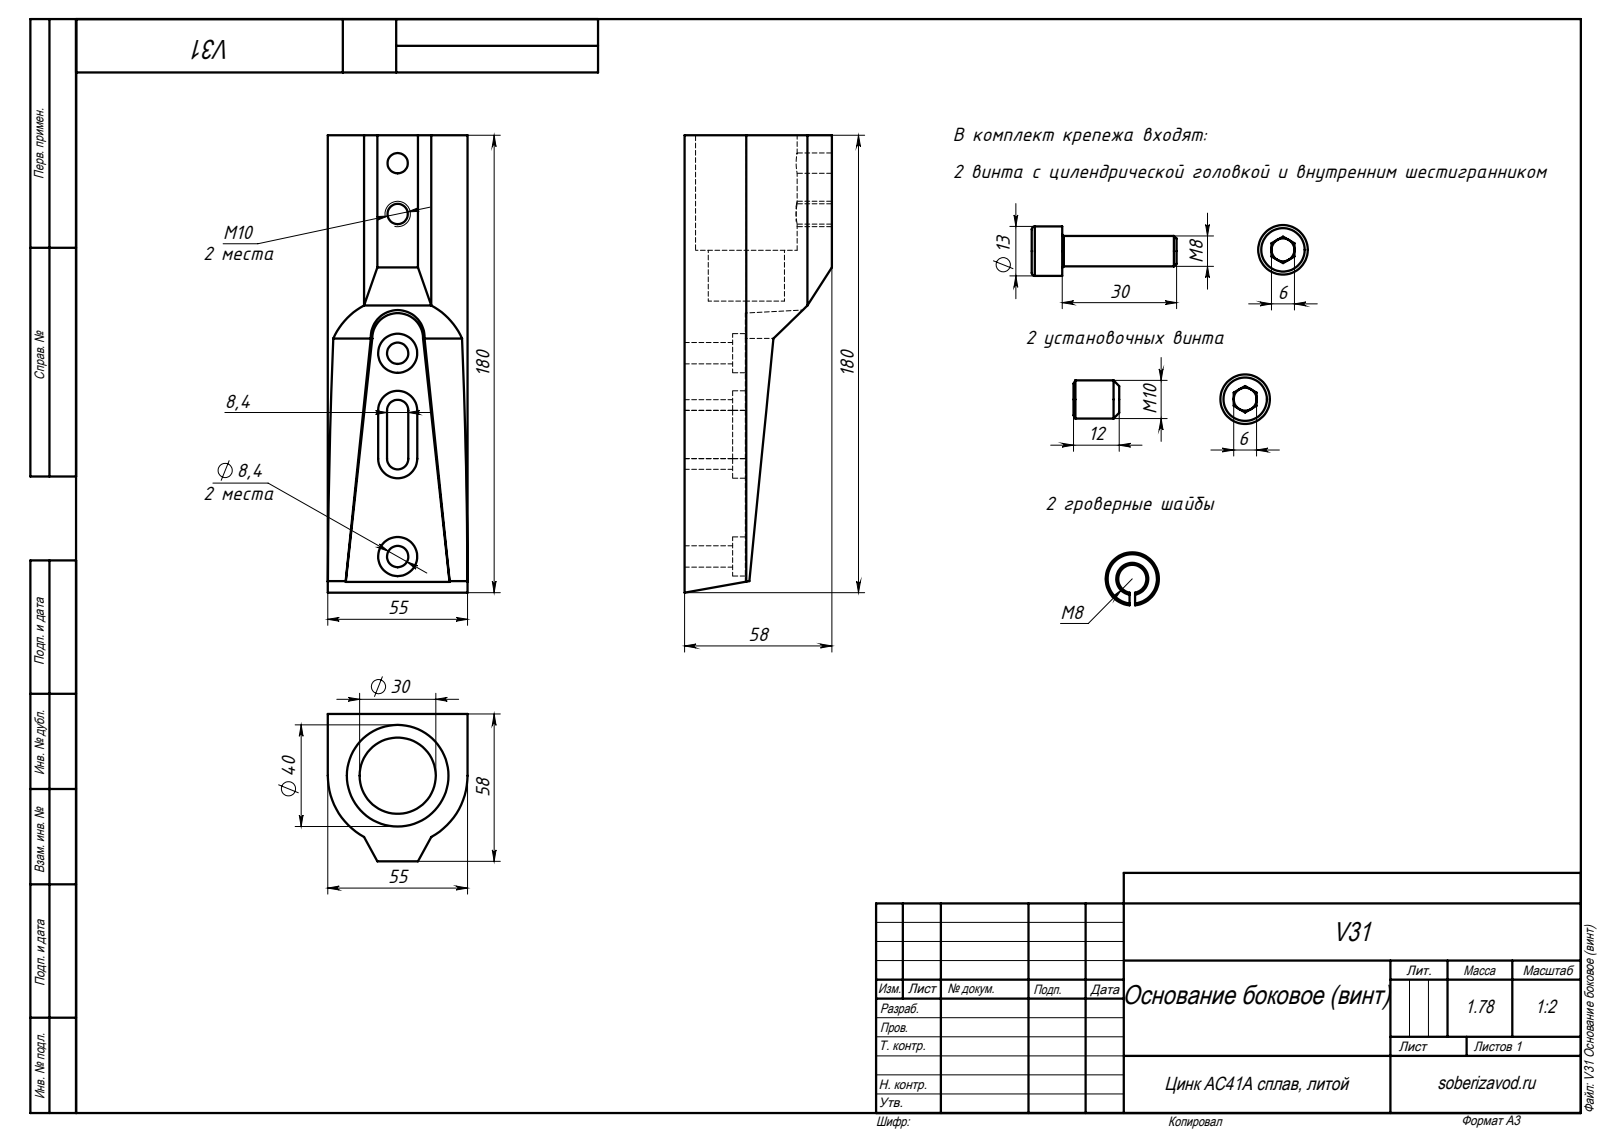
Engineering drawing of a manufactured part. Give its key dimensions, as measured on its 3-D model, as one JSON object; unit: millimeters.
{"part_name": "V31 Основание боковое (винт); curved spring lock washer_din_Spring washer DIN 128 - A8; socket set screw flat point_din_DIN 913 - M10 x 12-N; socket head cap screw_din_DIN 912 M8 x 30 --- 30N", "step_written_by": "SolidWorks 2018 (AUTOMOTIVE_DESIGN)", "units": "millimeters", "bodies": {"solids": 7, "faces": 150, "planar": 80, "cylindrical": 40, "other": 30}, "overall_size": [180, 67.5, 55], "volume_mm3": 271789, "surface_area_mm2": 53465, "round_holes": [[8, 2], [8.1, 2], [8.4, 2], [15.4, 2], [30, 1], [40, 1]], "round_bosses_or_shafts": [[14.8, 2], [13, 2], [10, 2], [8, 2]], "partial_cylinders_radius": [[4.2, 2], [7.7, 2], [27.5, 1]], "face_to_face_distances": [55, 23.9, 5, 58, 34.1, 18.9, 39.1, 23.3, 31.7, 65.3], "hole_center_spacings": [20, 54.8, 74.8, 80, 134.8, 154.8]}
